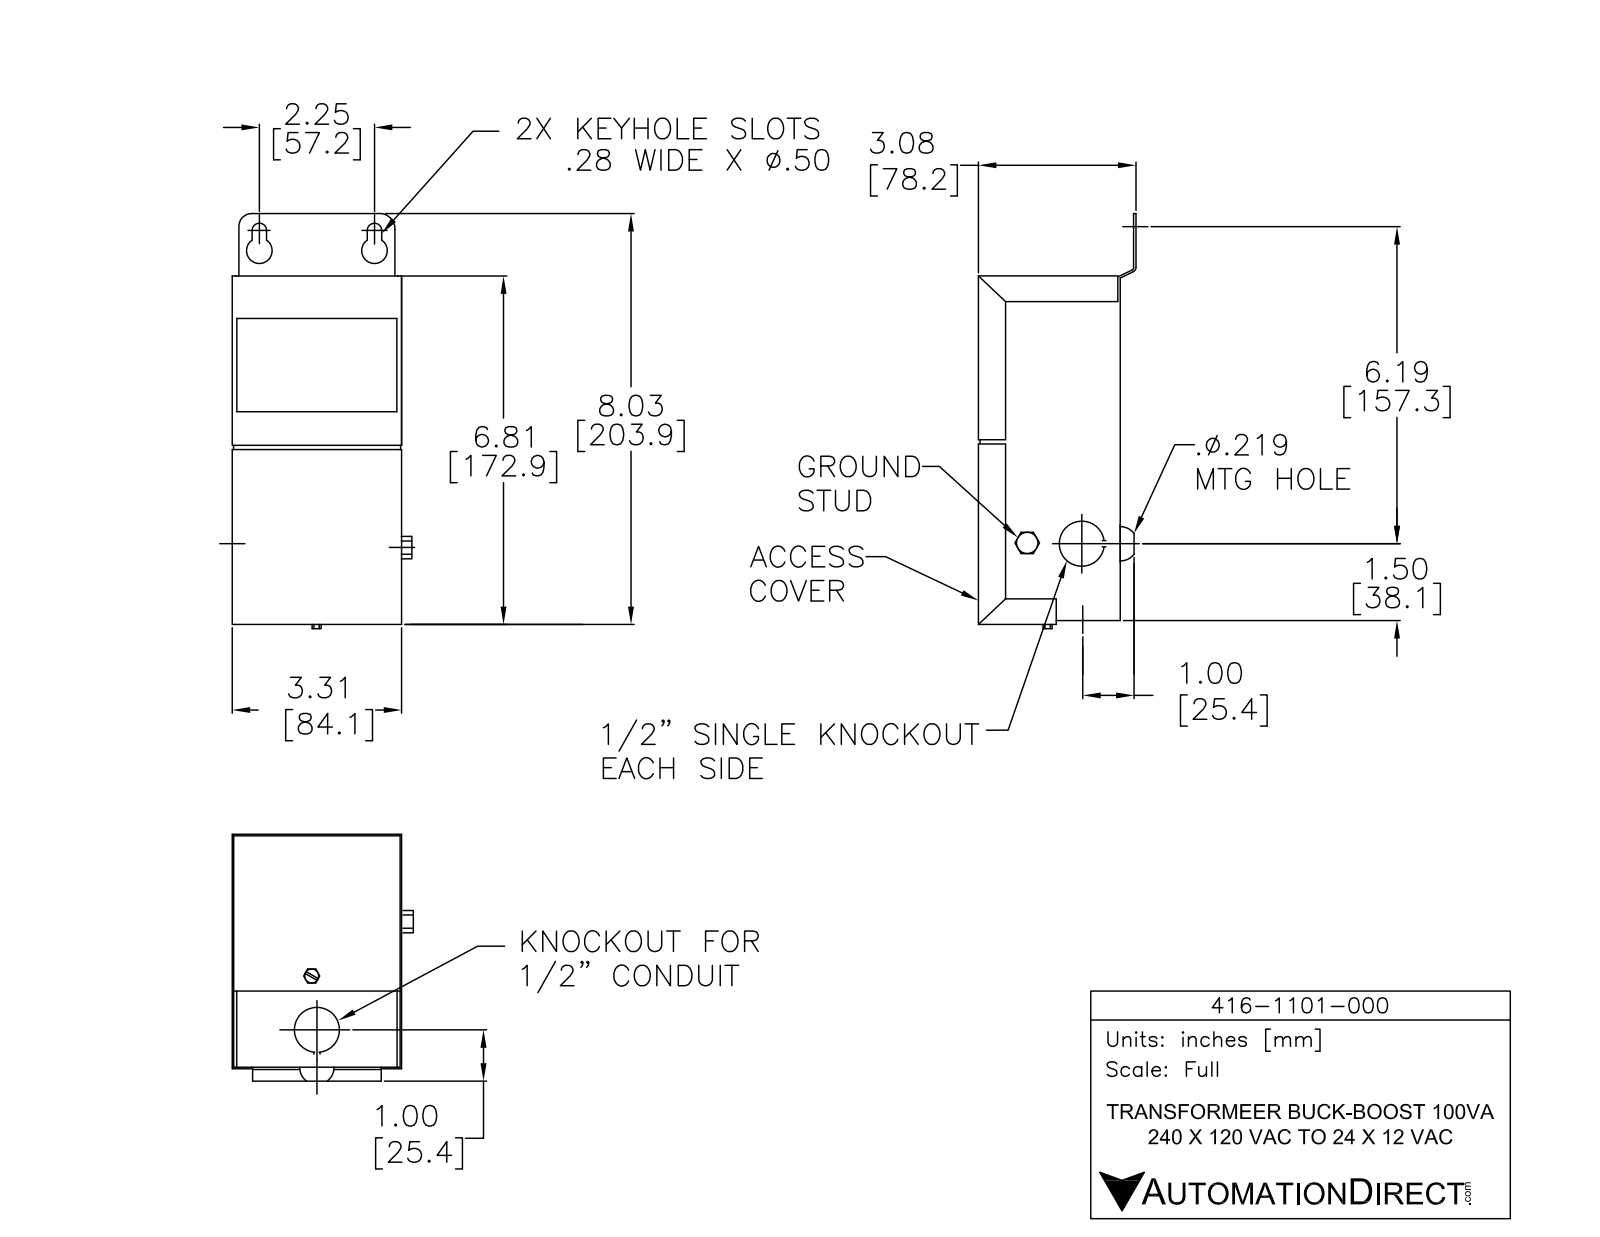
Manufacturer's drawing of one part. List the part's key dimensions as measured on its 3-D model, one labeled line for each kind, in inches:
Part name (STEP PRODUCT): 416-1101-000
STEP written by: SolidWorks 2013 (AUTOMOTIVE_DESIGN)
Units: inches
Bodies: 1 solid, 150 faces (89 planar, 45 cylindrical, 16 other)
Overall size (bounding box): 8.14 × 3.42 × 3.081
Volume: 63.4 in³ · Surface area: 112.7 in²
Round holes (diameter × count): ⌀0.5 ×2, ⌀0.875 ×2, ⌀0.185 ×1, ⌀0.231 ×1, ⌀0.275 ×1
Partial cylindrical surfaces — rounded edges, fillets, slot ends (radius × count): R0.04 ×10, R0.25 ×10, R0.14 ×2, R0.06 ×1, R0.1 ×1
Main face-to-face distances: 2.861, 3.23, 0.04, 3.27, 0.04, 2.86, 3.31, 6.81, 6.77, 0.22
Hole centre spacings: 5.908, 0.763, 0.862, 2.25
